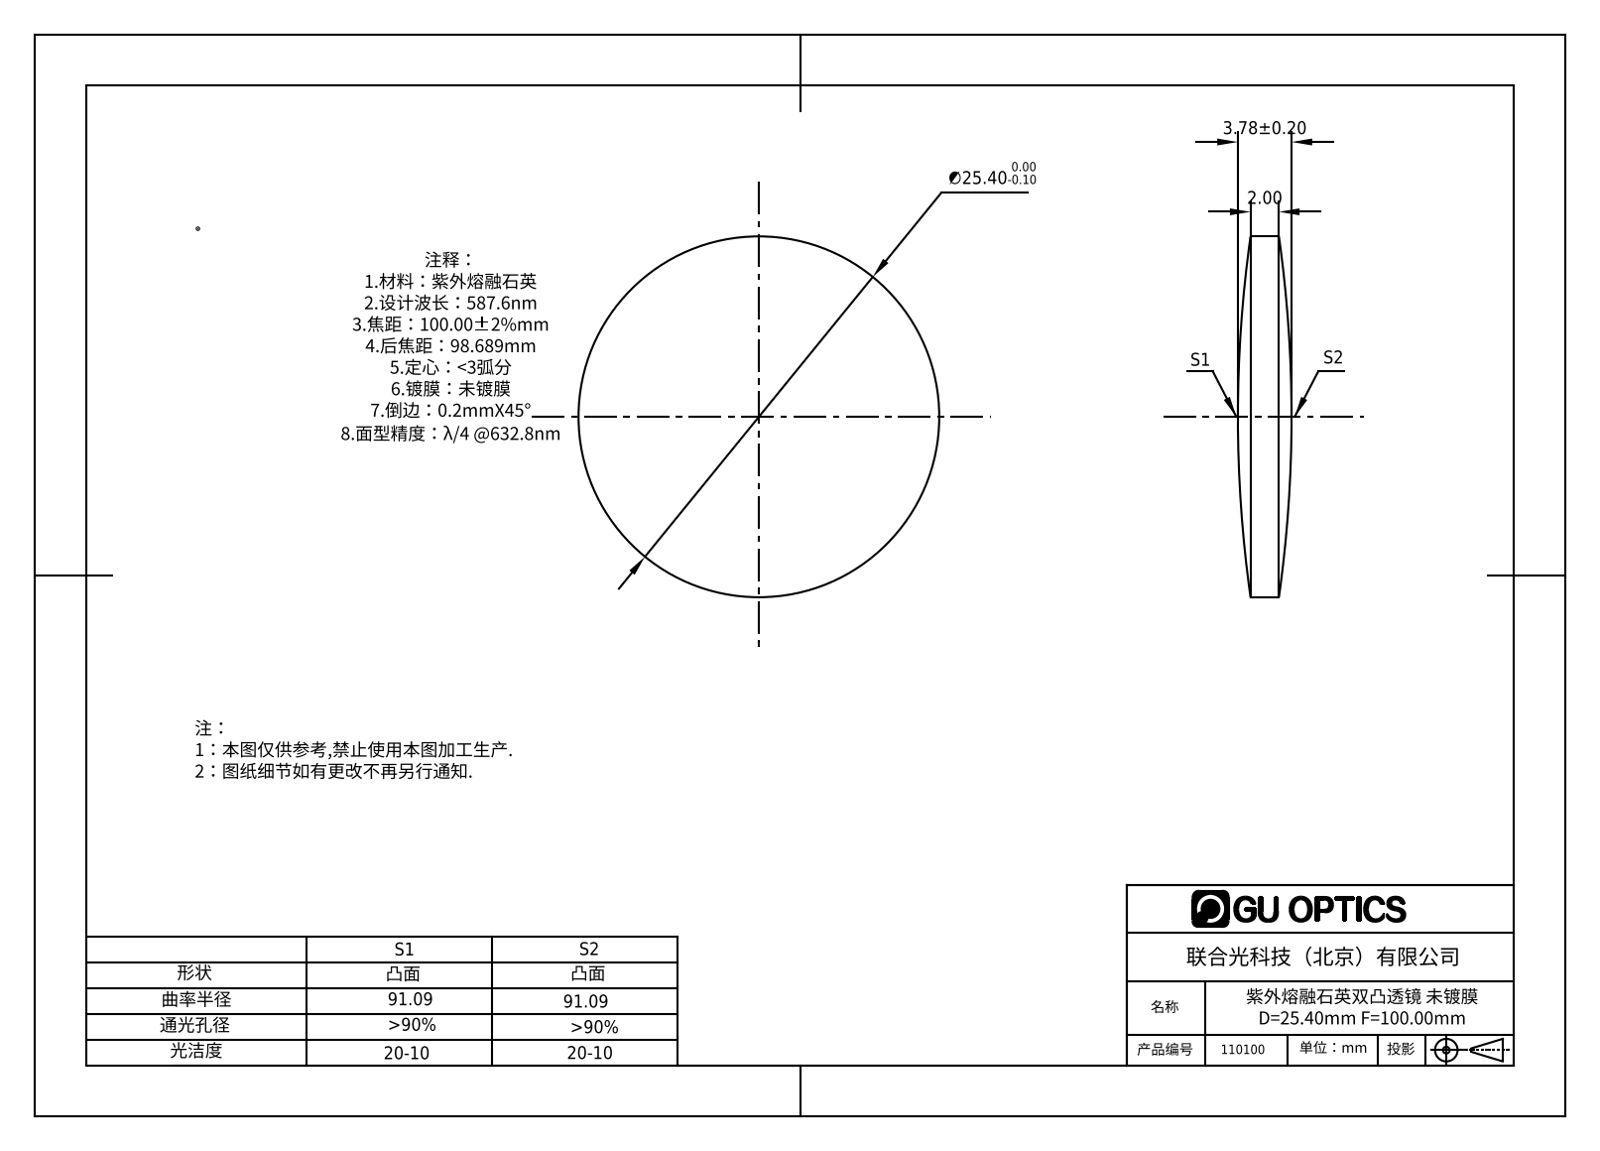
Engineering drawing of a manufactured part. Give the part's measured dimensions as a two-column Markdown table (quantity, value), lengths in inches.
| quantity | value |
| --- | --- |
| part name | 110100 |
| STEP written by | SolidWorks 2016 (CONFIG_CONTROL_DESIGN) |
| units | inches |
| bodies | 1 solid, 6 faces (0 planar, 2 cylindrical, 4 other) |
| overall size | 1 × 1 × 0.149 |
| volume | 0.089 in³ |
| surface area | 1.826 in² |
| round bosses / shafts (diameter × count) | 1 × 1 |
